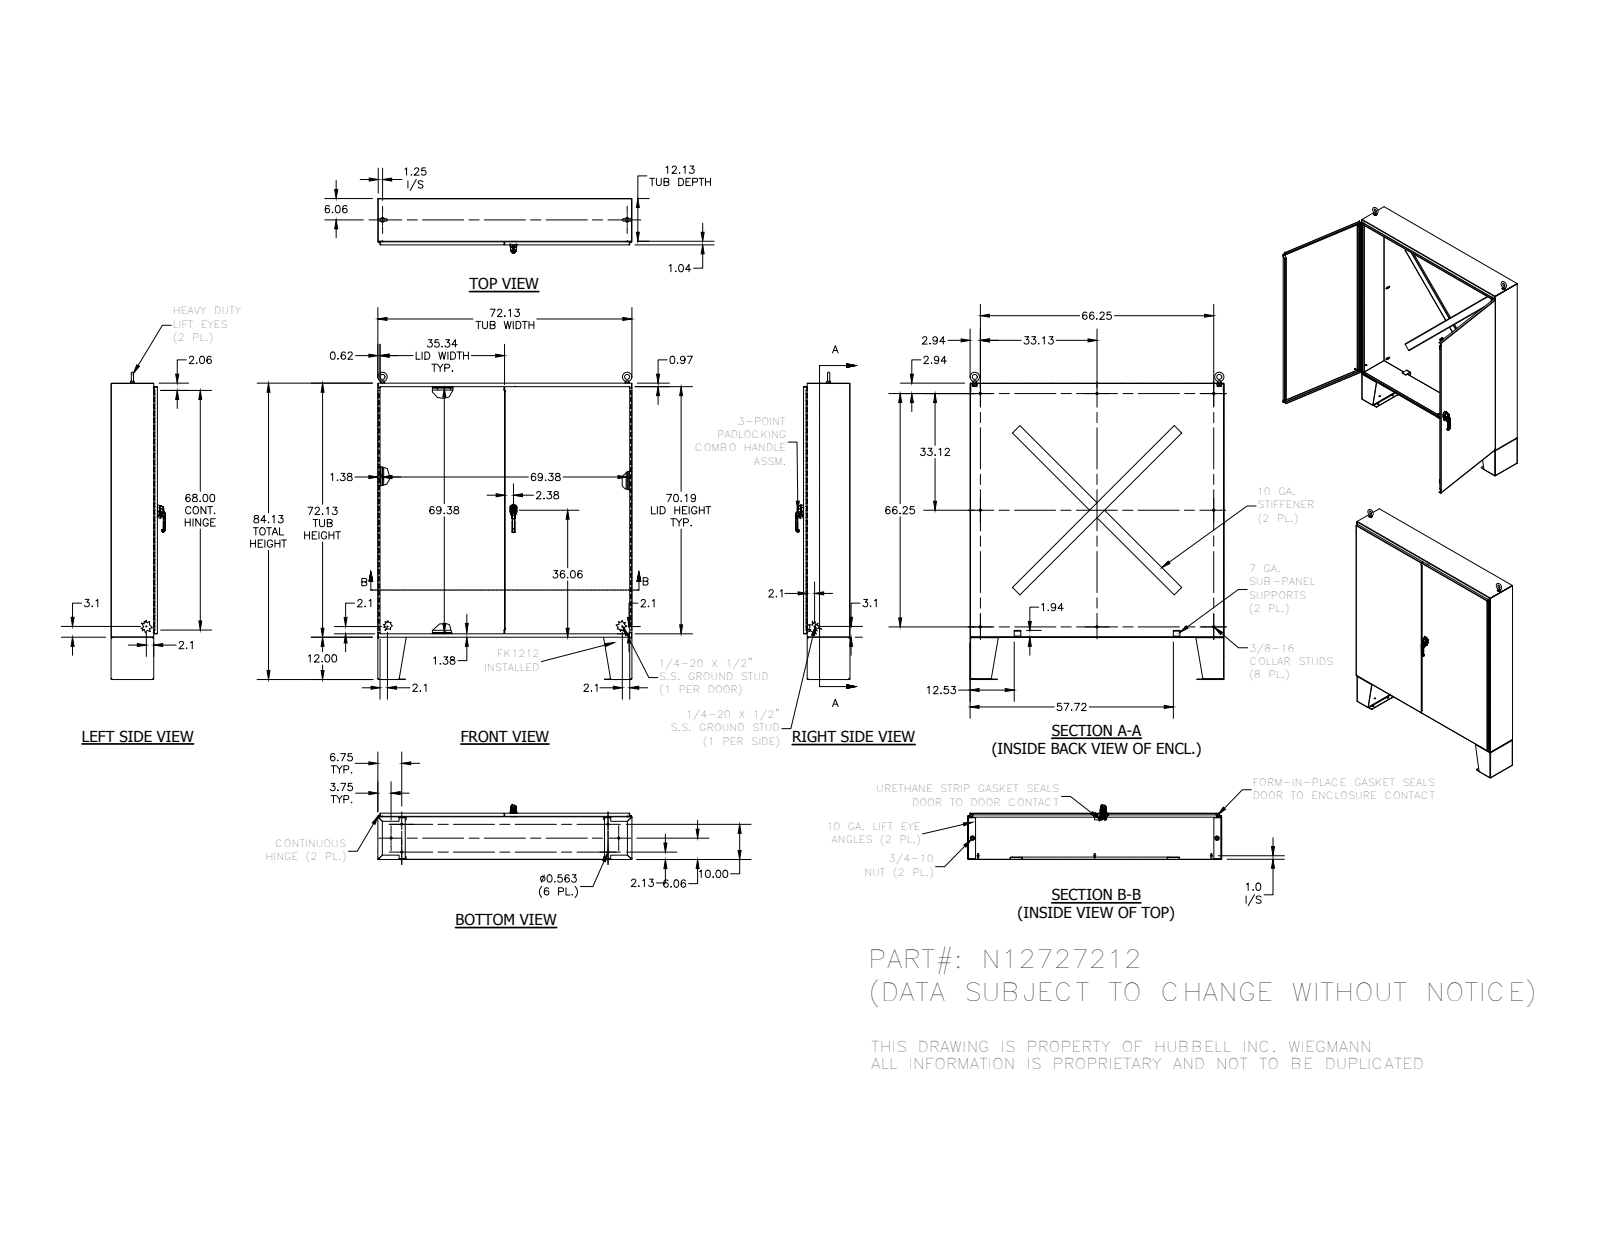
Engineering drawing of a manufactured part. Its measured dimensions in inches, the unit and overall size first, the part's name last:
Units: inches
Overall size (bounding box): 87.248 × 73.785 × 15.338
Round holes (diameter × count): ⌀0.563 ×18, ⌀0.277 ×8, ⌀0.2 ×4, ⌀0.28 ×3, ⌀0.125 ×2, ⌀0.125 ×2, ⌀0.241 ×2, ⌀0.25 ×2, ⌀0.252 ×2, ⌀0.4 ×2, ⌀0.45 ×2, ⌀0.642 ×2
Round bosses / shafts (diameter × count): ⌀0.33 ×8, ⌀0.25 ×5, ⌀0.625 ×4, ⌀0.625 ×4, ⌀0.337 ×3, ⌀1.25 ×2, ⌀1.12 ×2, ⌀1 ×2
Partial cylindrical surfaces — rounded edges, fillets, slot ends (radius × count): R0.031 ×24, R0.094 ×23, R0.219 ×22, R0.05 ×18, R0.025 ×16, R0.125 ×15, R0.03 ×13, R0.067 ×8
Main face-to-face distances: 0.094, 13.067, 12.973, 13.16, 72.031, 72.125, 71.938, 0.125, 12.125, 0.942
Hole centre spacings: 1.459, 2.041, 4.963, 5, 6.688, 9.281, 9.316, 10.454
Volume: 1 688 in³ · Surface area: 34 233 in²
Bodies: 76 solids, 2596 faces (1528 planar, 768 cylindrical, 300 other)
Part name (STEP PRODUCT): N12727212
STEP written by: SolidWorks 2018 (AUTOMOTIVE_DESIGN)
